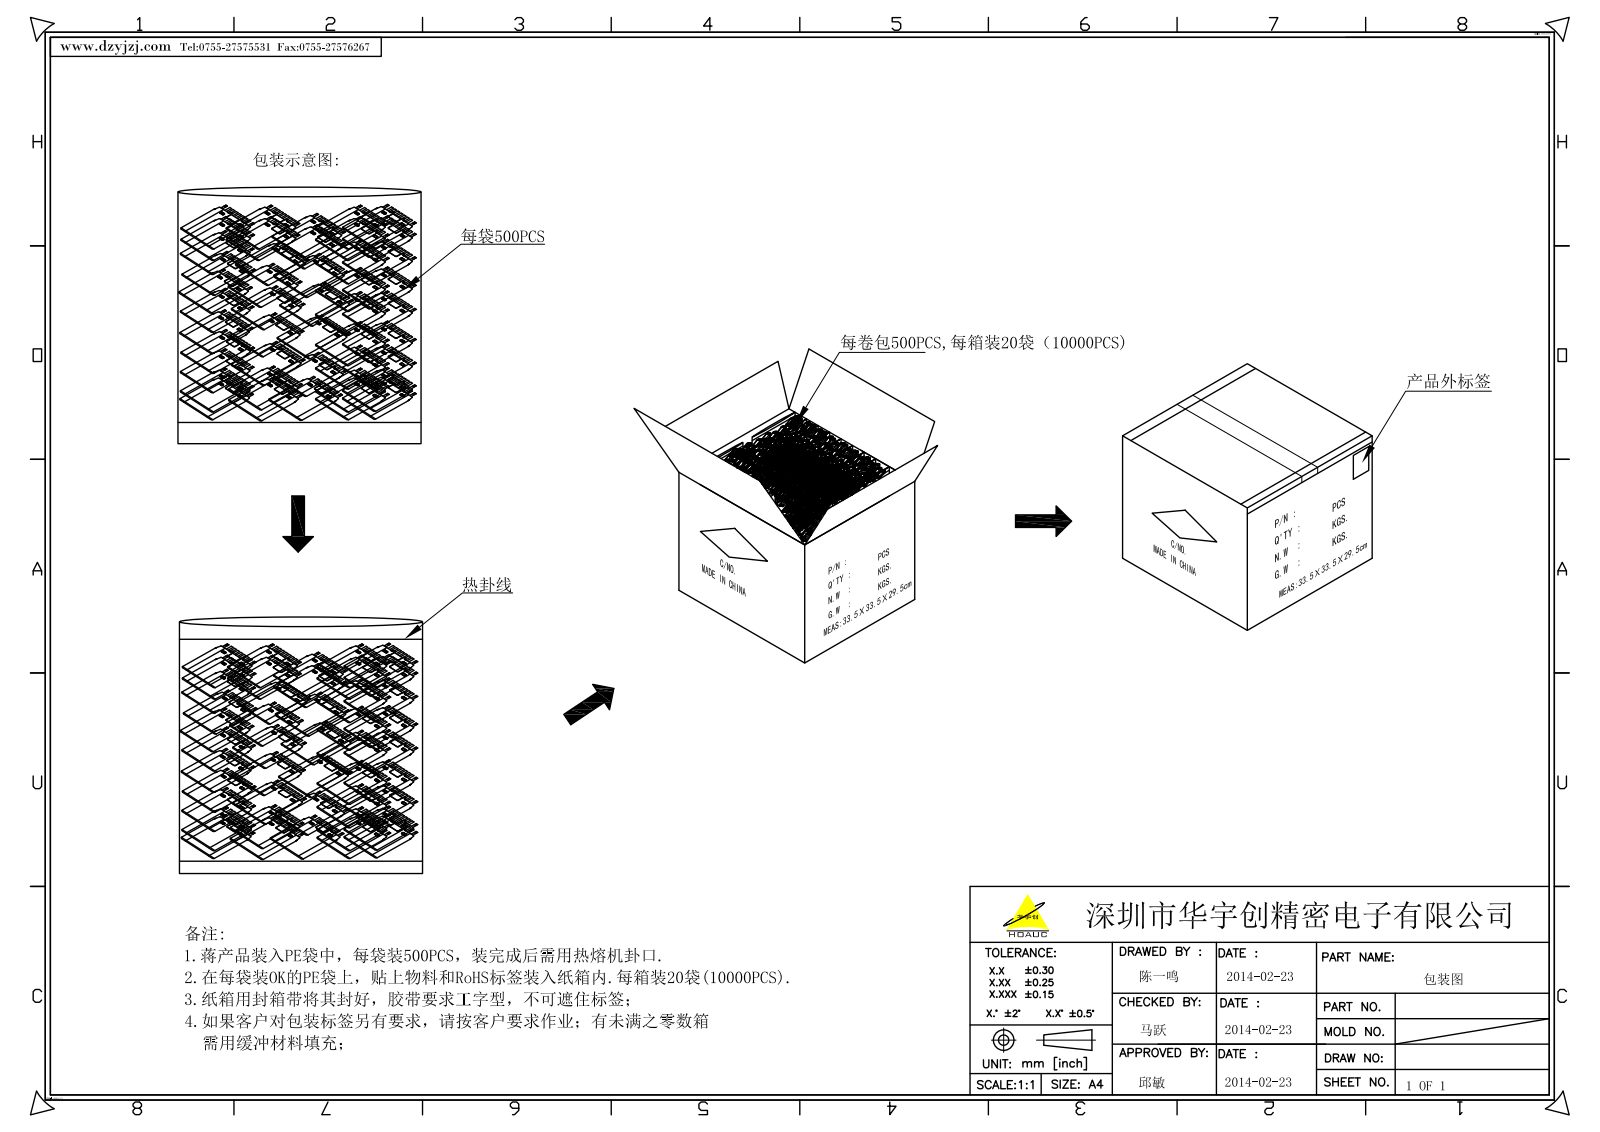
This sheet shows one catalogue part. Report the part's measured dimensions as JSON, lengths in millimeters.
{"part_name": "TANPIAN-PLASTIC_1_2__2_30_1_1_2", "step_written_by": "CREO PARAMETRIC BY PTC INC, 2022073 (AUTOMOTIVE_DESIGN)", "units": "millimeters", "bodies": {"solids": 1, "faces": 783, "planar": 537, "cylindrical": 242, "other": 4}, "overall_size": [13, 8.25, 2.42], "volume_mm3": 174, "surface_area_mm2": 450, "round_holes": [[0.6, 2]], "partial_cylinders_radius": [[0.15, 55], [0.13, 16], [0.2, 10], [0.3, 10], [0.25, 6], [1.05, 6], [0.1, 3], [0.18, 2]], "face_to_face_distances": [2.4, 0.8, 0.81, 1.61, 0.79, 1.59, 1.05, 0.56, 1.08, 1.84], "hole_center_spacings": [4.6]}
